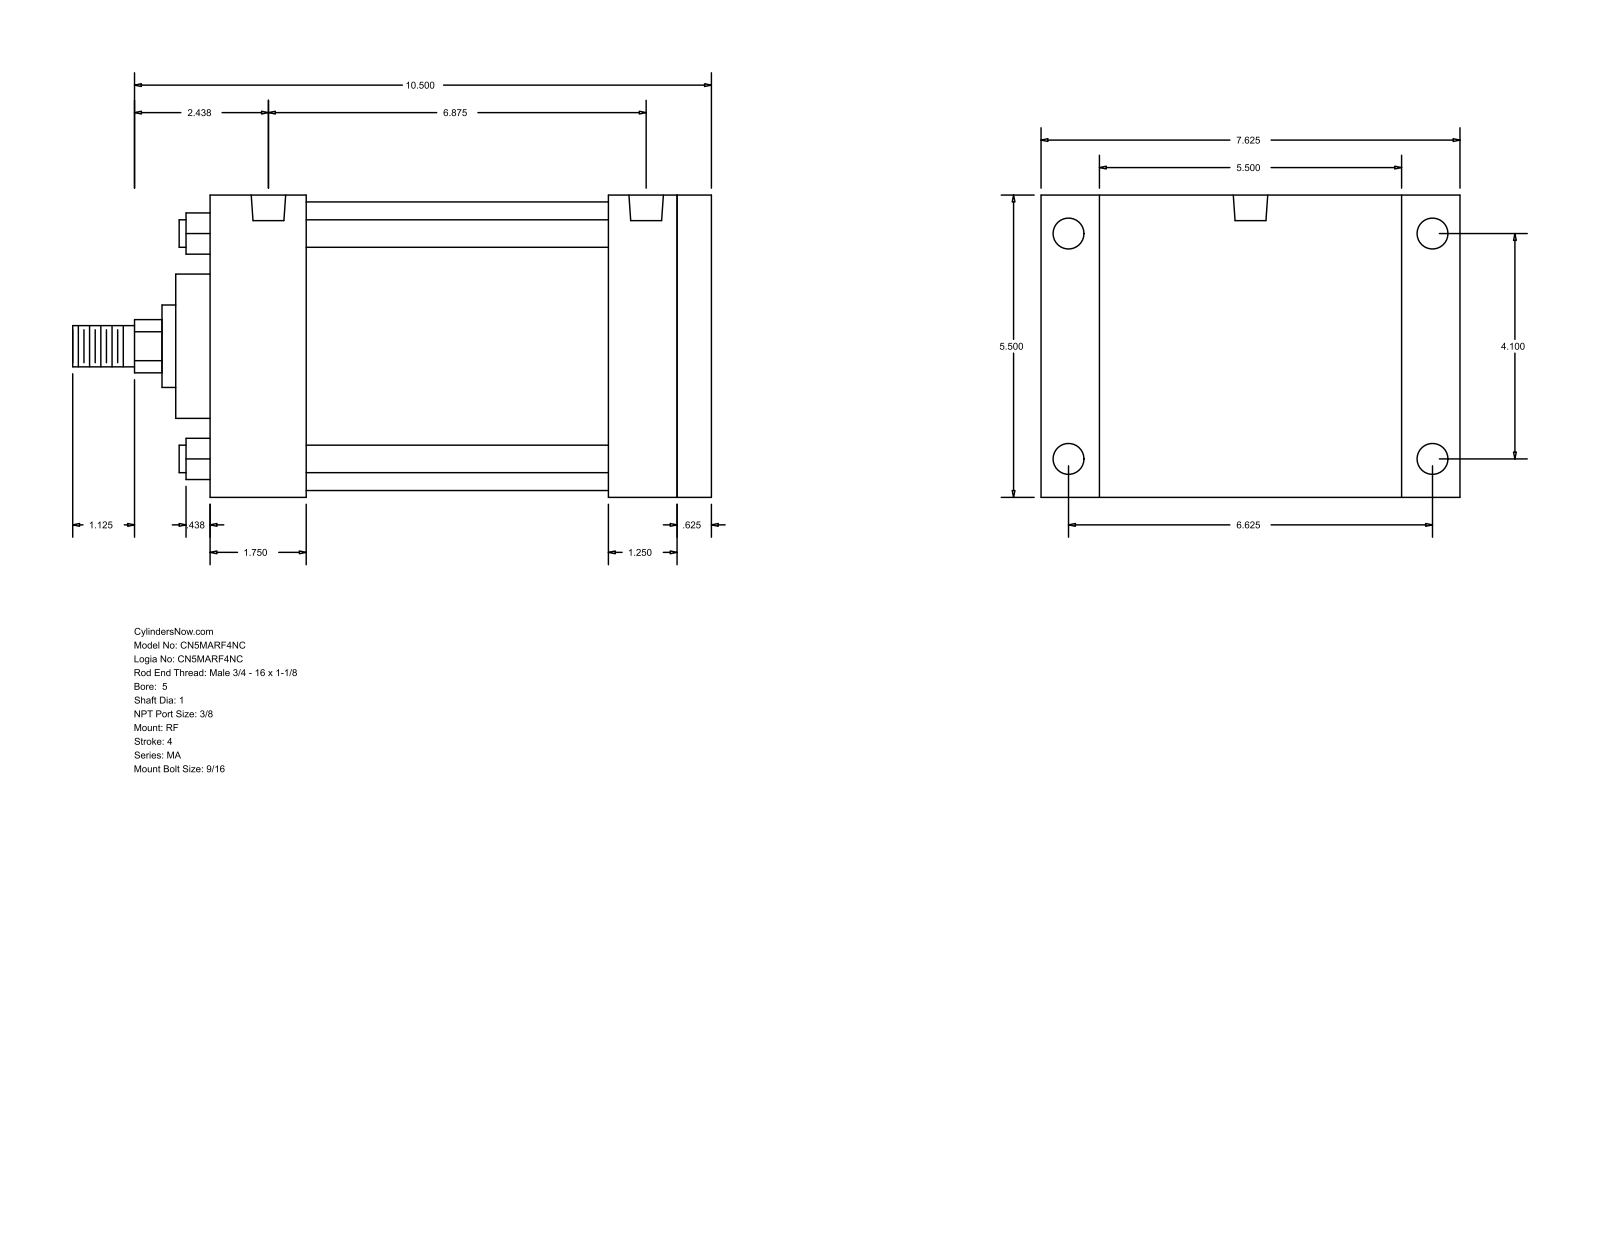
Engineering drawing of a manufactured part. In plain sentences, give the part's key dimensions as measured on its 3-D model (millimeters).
The part is named "MA_RF__0500_1". Its 3-D file was written by "GSSL Pune (CONFIG_CONTROL_DESIGN)". It is 0 solids with 94 faces: 65 planar, 29 cylindrical and 0 other. Overall it measures 295.27 by 193.68 by 139.7 millimeters. Round holes: 4 of diameter 11.11, 4 of diameter 14.29, 2 of diameter 15.93. Round bosses or shafts: 4 of diameter 12.7, 1 of diameter 133.35, 1 of diameter 66.67, 1 of diameter 38.1, 1 of diameter 25.4, 1 of diameter 19.05. Partial cylindrical surfaces (rounded edges, fillets, slot ends): 1 of radius 12.29. The main face-to-face distances are 139.7, 231.78, 215.9, 15.88, 44.46, 171.44, 187.32, 184.15, 139.69, 31.75. The hole center spacings are 4.76, 104.14, 165.11, 168.28, 169.87, 197.9, 174.63.
